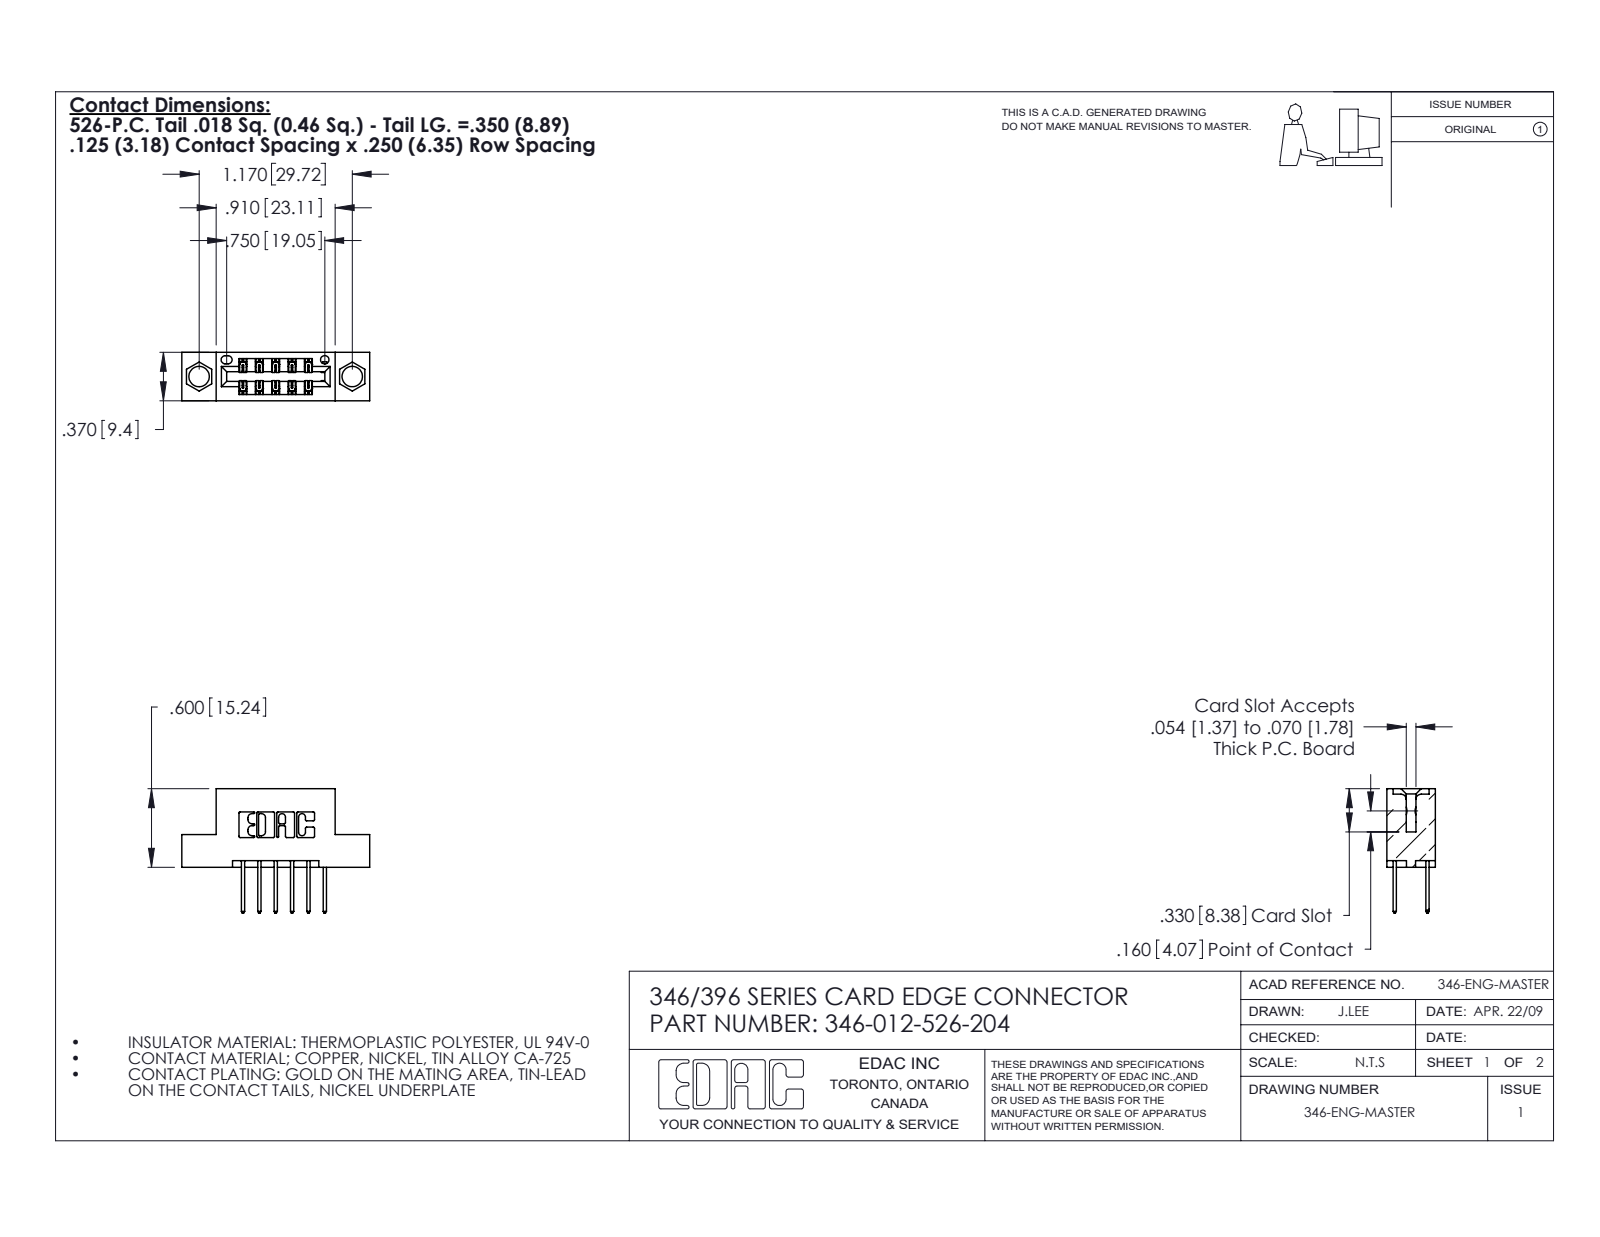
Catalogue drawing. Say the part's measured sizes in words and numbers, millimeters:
The part is named "345-292-001_345-293-126; 346 Part_Flush Mounting Lugs - 0.156 Dia-TH; 346-012-526-204". Its 3-D file was written by "SolidWorks 2020 (CONFIG_CONTROL_DESIGN)". It is 13 solids with 748 faces: 500 planar, 248 cylindrical and 0 other. Overall it measures 36.4 by 24.1 by 9.4 millimeters. Its volume is 3 200 cubic millimeters and its surface area 3 855 square millimeters. Round holes: 2 of diameter 4, 1 of diameter 1.6. Partial cylindrical surfaces (rounded edges, fillets, slot ends): 22 of radius 0.3, 18 of radius 0.2, 12 of radius 0.3, 6 of radius 0.2, 6 of radius 0.8, 3 of radius 0.7, 2 of radius 0.4, 2 of radius 0.6. The main face-to-face distances are 6.4, 1.2, 8.2, 9.4, 0.6, 1.8, 7.6, 7, 3.8, 5.6. The hole center spacings are 6.2, 24.6, 29.7.
